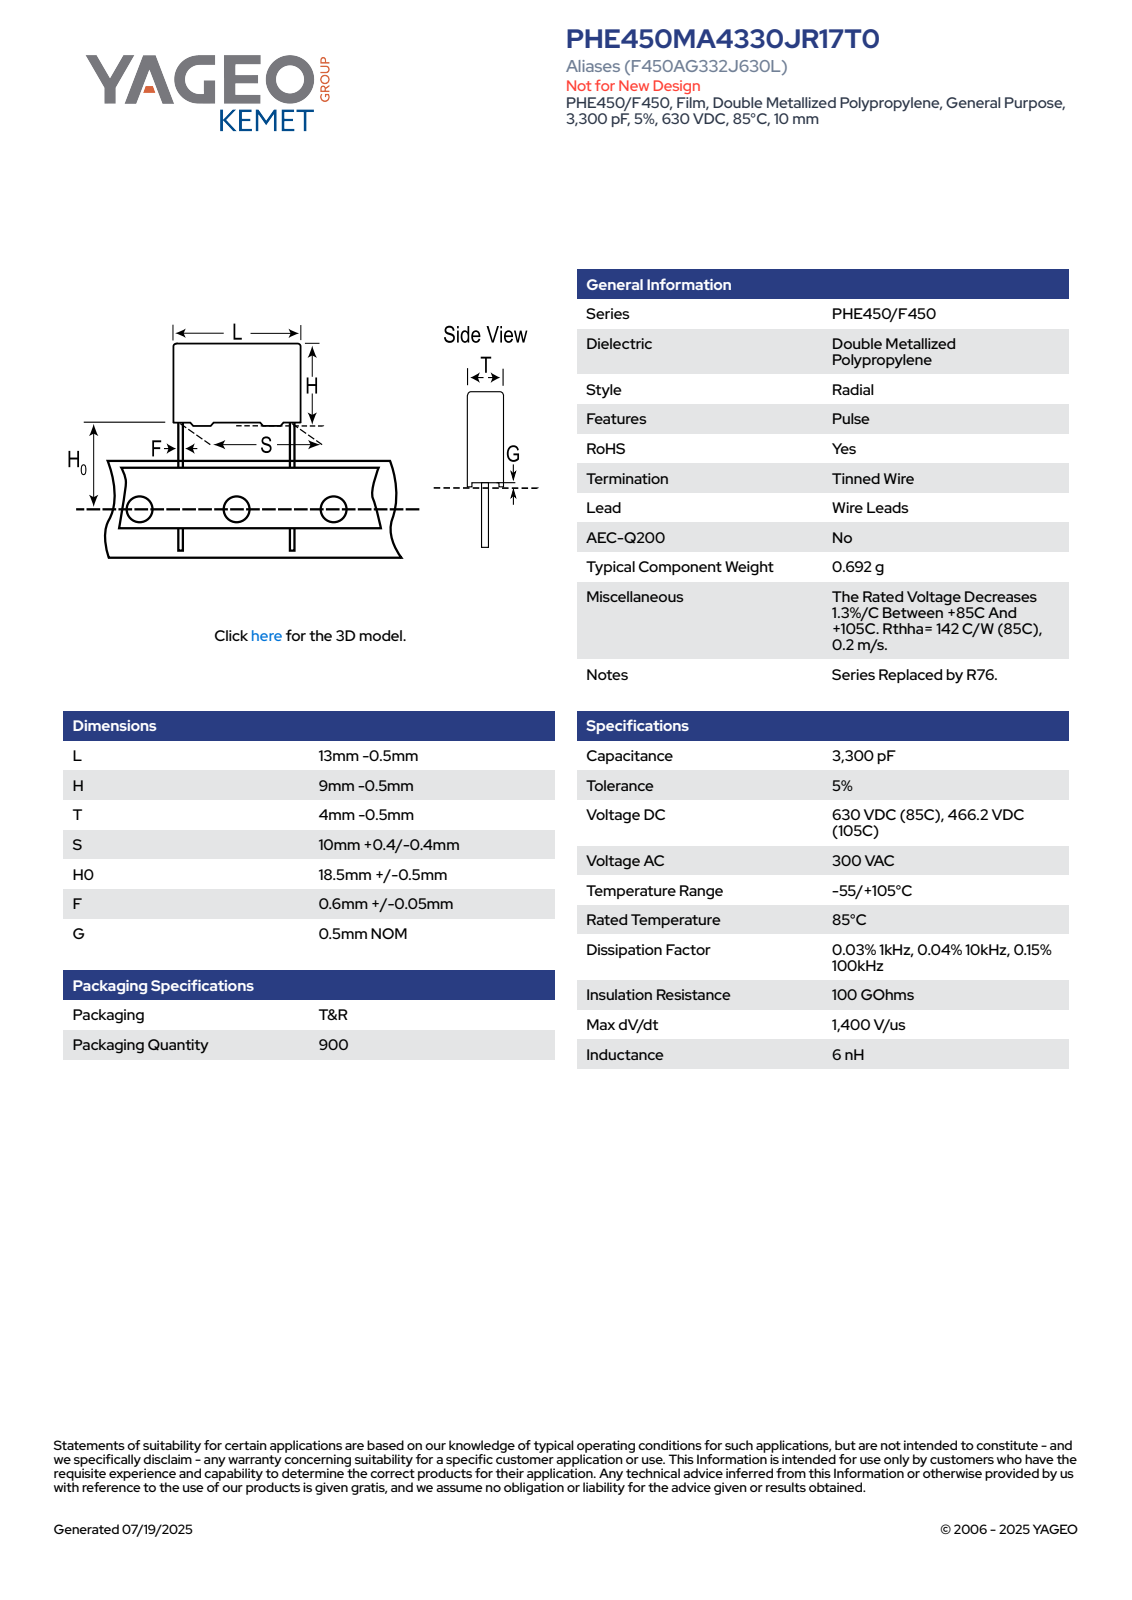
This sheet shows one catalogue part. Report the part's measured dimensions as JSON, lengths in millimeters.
{"part_name": "CFR_RBG_13X9X4_L12.5H8.5T3.5S10H019F0.65G0.5", "step_written_by": "SolidWorks 2014 (AUTOMOTIVE_DESIGN)", "units": "millimeters", "bodies": {"solids": 4, "faces": 89, "planar": 81, "cylindrical": 8, "other": 0}, "overall_size": [27.5, 12.5, 3.5], "volume_mm3": 362, "surface_area_mm2": 442, "round_bosses_or_shafts": [[0.65, 2]], "partial_cylinders_radius": [[0.5, 4]], "face_to_face_distances": [3.5, 8, 12.5, 3.3, 3.1, 0.5, 8.5, 19, 19.5, 27.5]}
